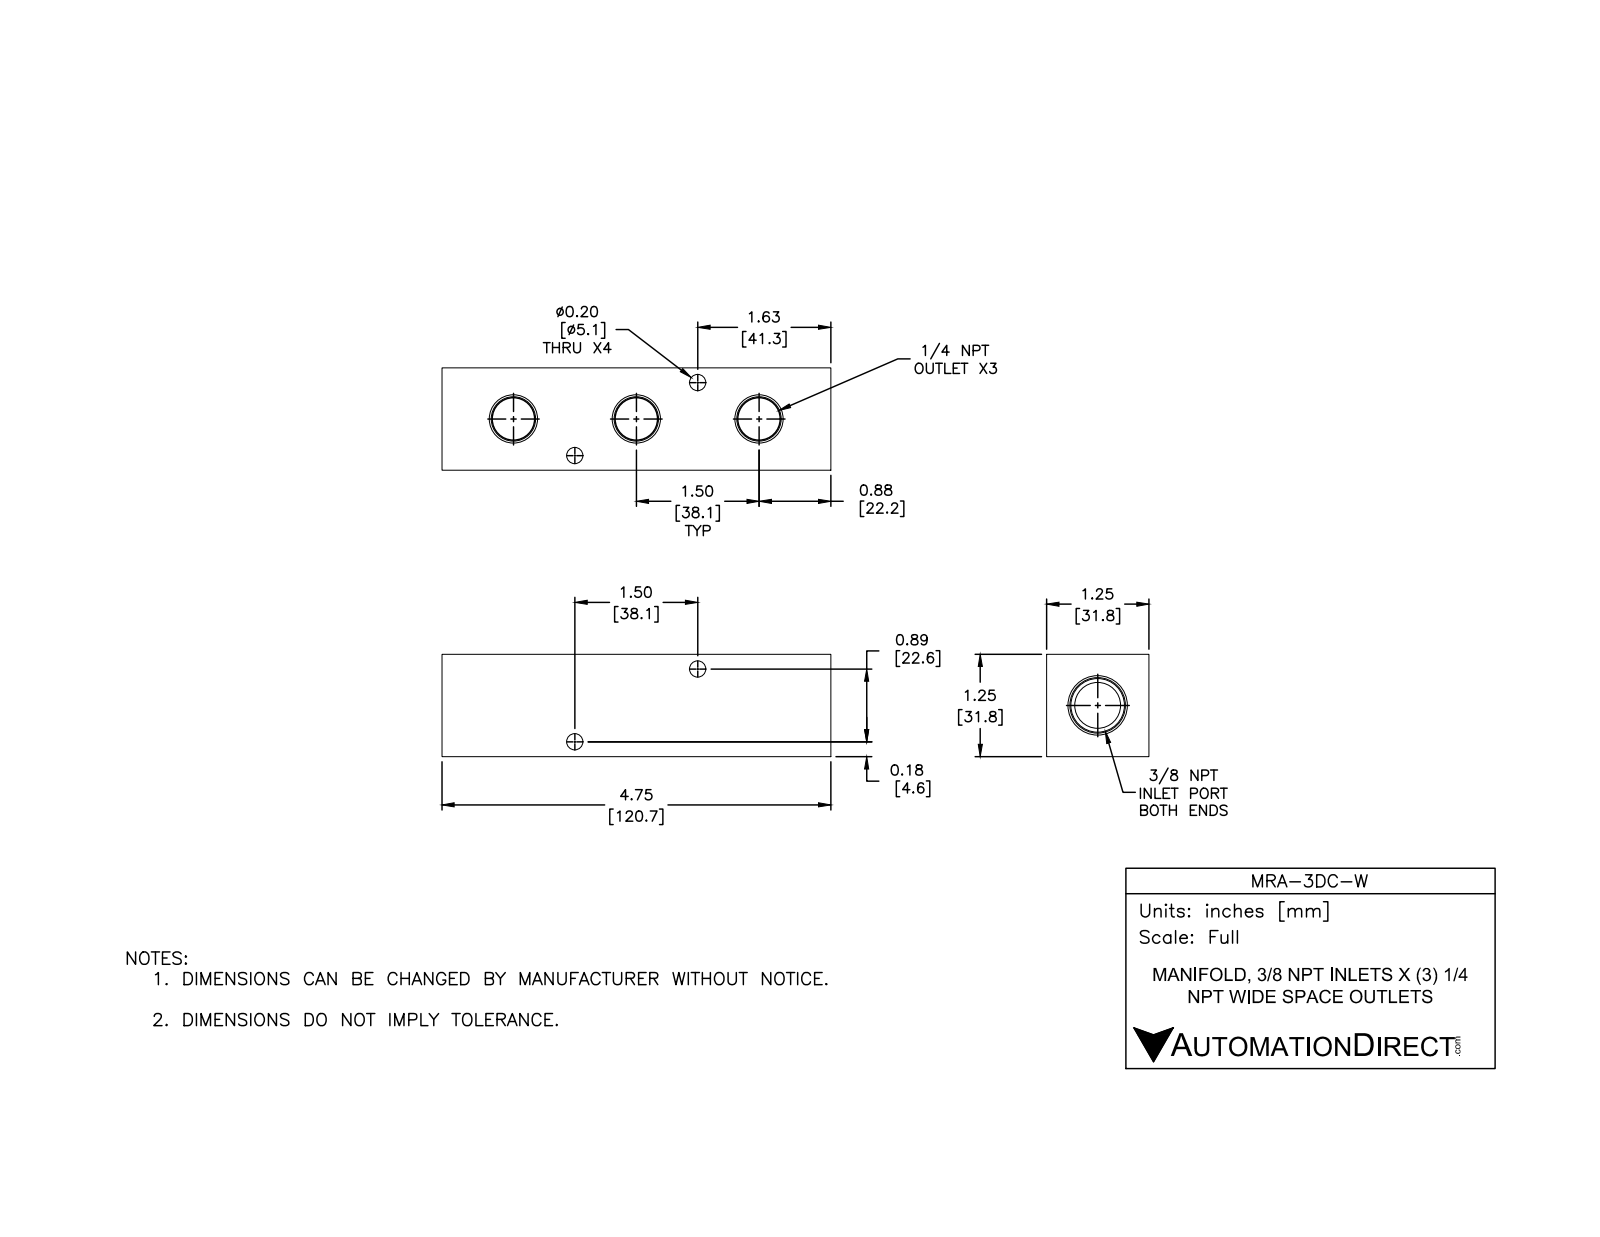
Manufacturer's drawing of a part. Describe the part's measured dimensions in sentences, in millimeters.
The part is named "MRA-3DC-W". Its 3-D file was written by "SolidWorks 2015 (CONFIG_CONTROL_DESIGN)". It is 1 solid with 58 faces: 14 planar, 24 cylindrical and 20 other. Overall it measures 120.7 by 31.8 by 31.8 millimeters. Its volume is 94 520 cubic millimeters and its surface area 24 650 square millimeters. Round holes: 4 of diameter 5.1, 1 of diameter 14.3. Partial cylindrical surfaces (rounded edges, fillets, slot ends): 3 of radius 5.6. The main face-to-face distances are 31.8, 120.7, 10.4, 110.2, 21.8, 9.9, 99.8. The hole center spacings are 44.3.
